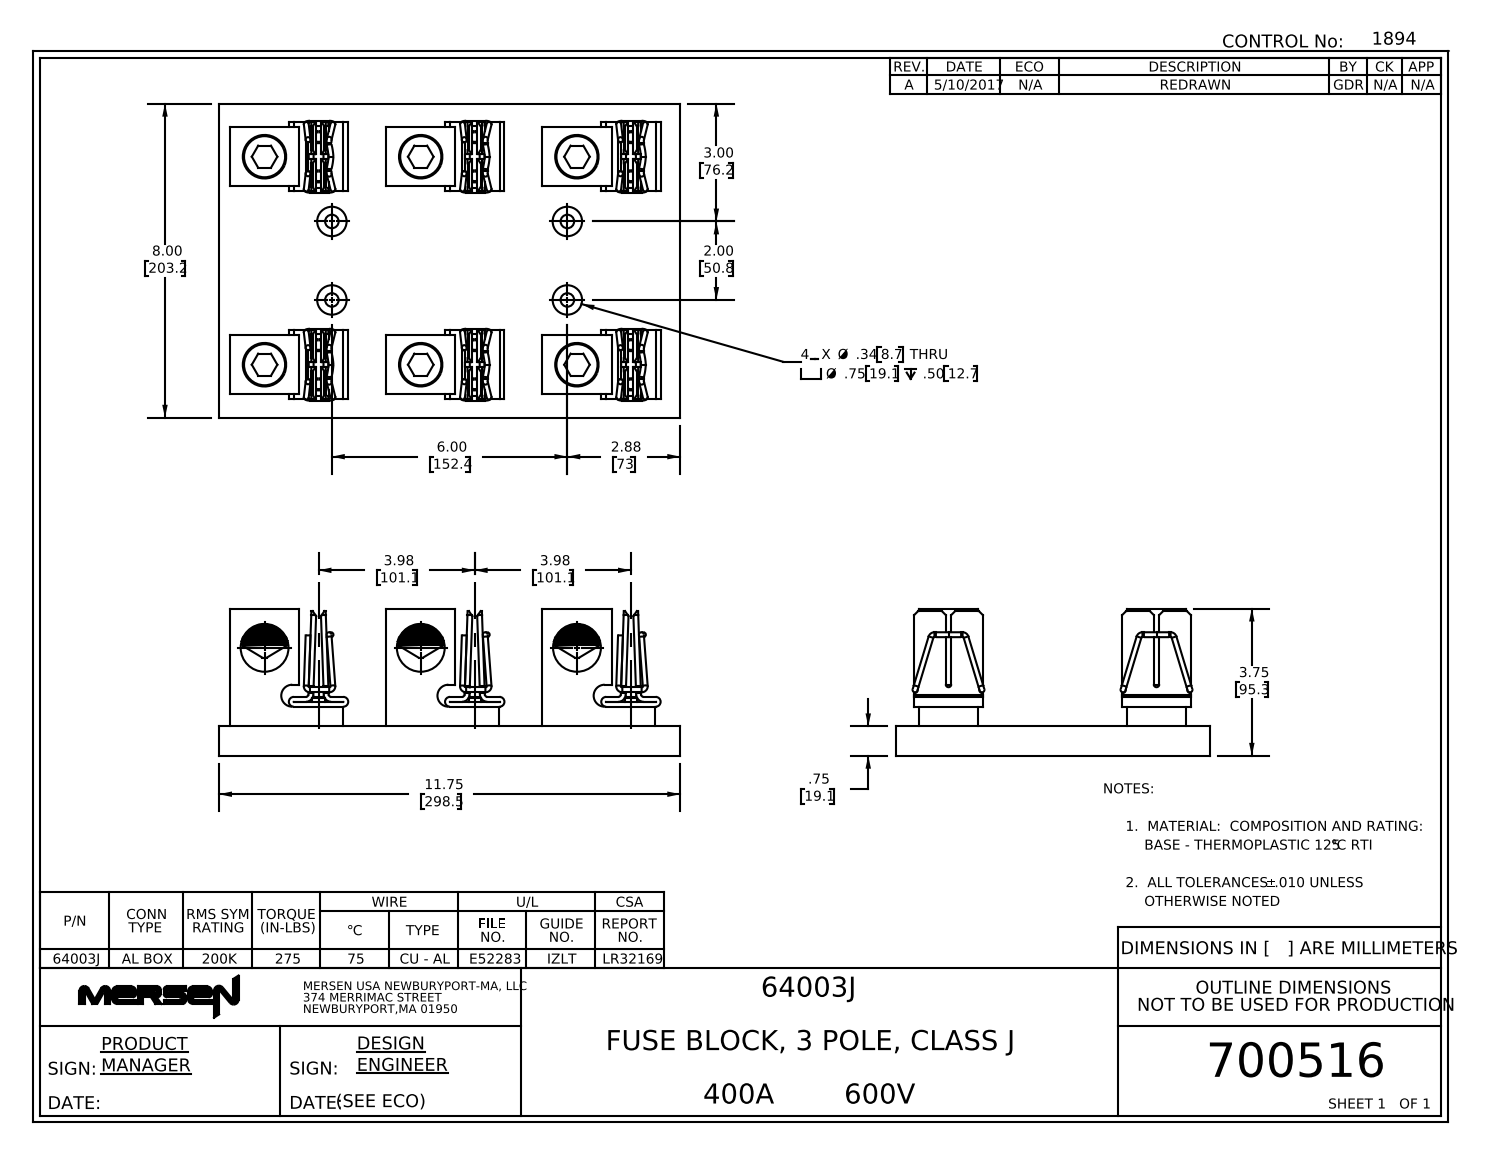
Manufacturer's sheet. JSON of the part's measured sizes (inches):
{"part_name": "700516revA", "step_written_by": "SolidWorks 2016 (AUTOMOTIVE_DESIGN)", "units": "inches", "bodies": {"solids": 49, "faces": 1440, "planar": 598, "cylindrical": 380, "other": 462}, "overall_size": [11.75, 8, 3.75], "volume_in3": 119, "surface_area_in2": 717.8, "round_holes": [[0.257, 12], [0.266, 12], [0.339, 12], [0.377, 12], [0.85, 12], [0.625, 7], [1.047, 6], [0.625, 5], [0.344, 4], [0.75, 4], [1.218, 3]], "round_bosses_or_shafts": [[1.095, 84], [0.313, 24], [1.17, 6]], "partial_cylinders_radius": [[0.063, 6], [0.125, 6], [0.187, 6], [0.094, 4], [0.28, 3], [0.069, 2]], "face_to_face_distances": [0.75, 3.976, 0.124, 5.3, 1.5, 3.98, 0.5, 1.25, 3.852, 0.124], "hole_center_spacings": [3.98, 5.3, 6.628, 1, 0.594, 1.945, 3.694, 5.881]}
